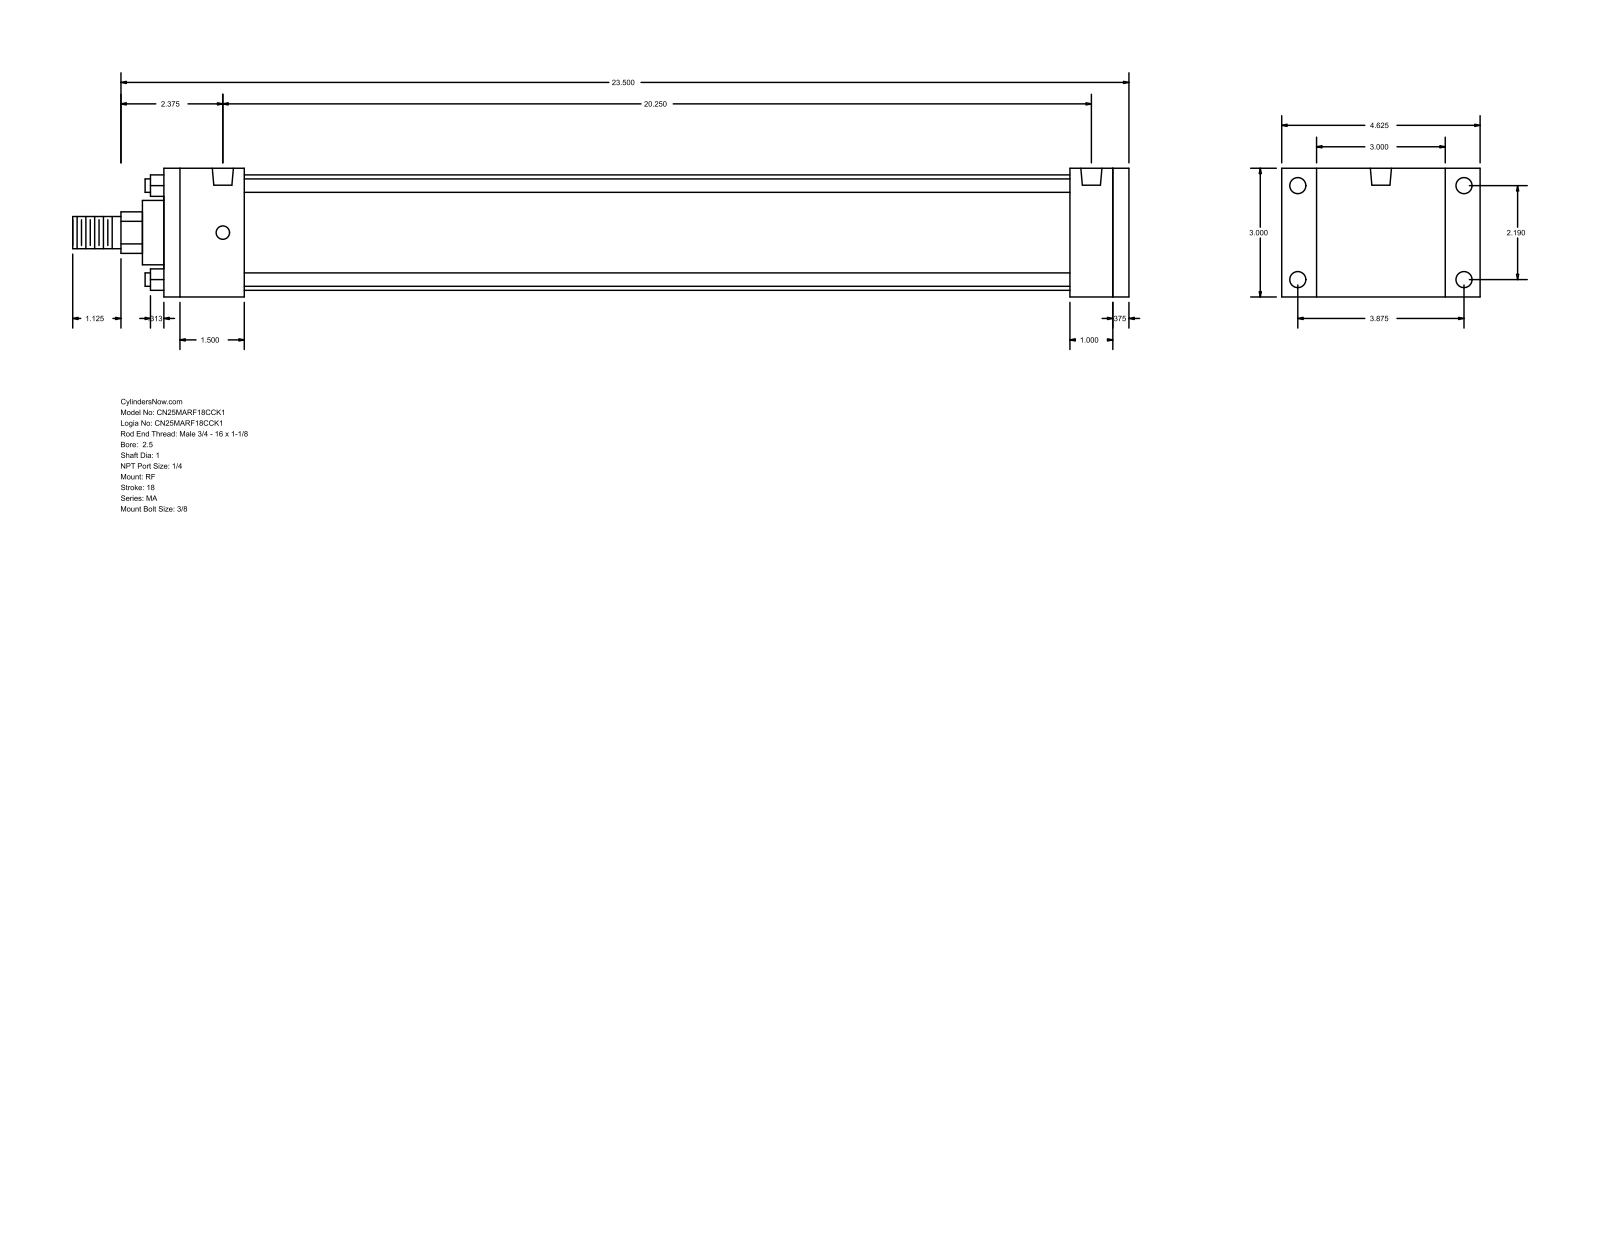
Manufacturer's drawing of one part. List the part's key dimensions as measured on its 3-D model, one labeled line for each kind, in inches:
Part name (STEP PRODUCT): MA_RF__0250_1
STEP written by: GSSL Pune (CONFIG_CONTROL_DESIGN)
Units: inches
Bodies: 0 solids, 92 faces (64 planar, 28 cylindrical, 0 other)
Overall size (bounding box): 24.625 × 4.625 × 3
Round holes (diameter × count): ⌀0.313 ×4, ⌀0.375 ×4, ⌀0.492 ×2
Round bosses / shafts (diameter × count): ⌀0.313 ×4, ⌀2.69 ×1, ⌀1.5 ×1, ⌀1 ×1, ⌀0.75 ×1
Partial cylindrical surfaces — rounded edges, fillets, slot ends (radius × count): R0.484 ×1
Main face-to-face distances: 3, 22.5, 22.125, 0.375, 1, 1.875, 21.125, 19.25, 20.25, 20.625
Hole centre spacings: 2.19, 3.875, 4.451, 20.25
